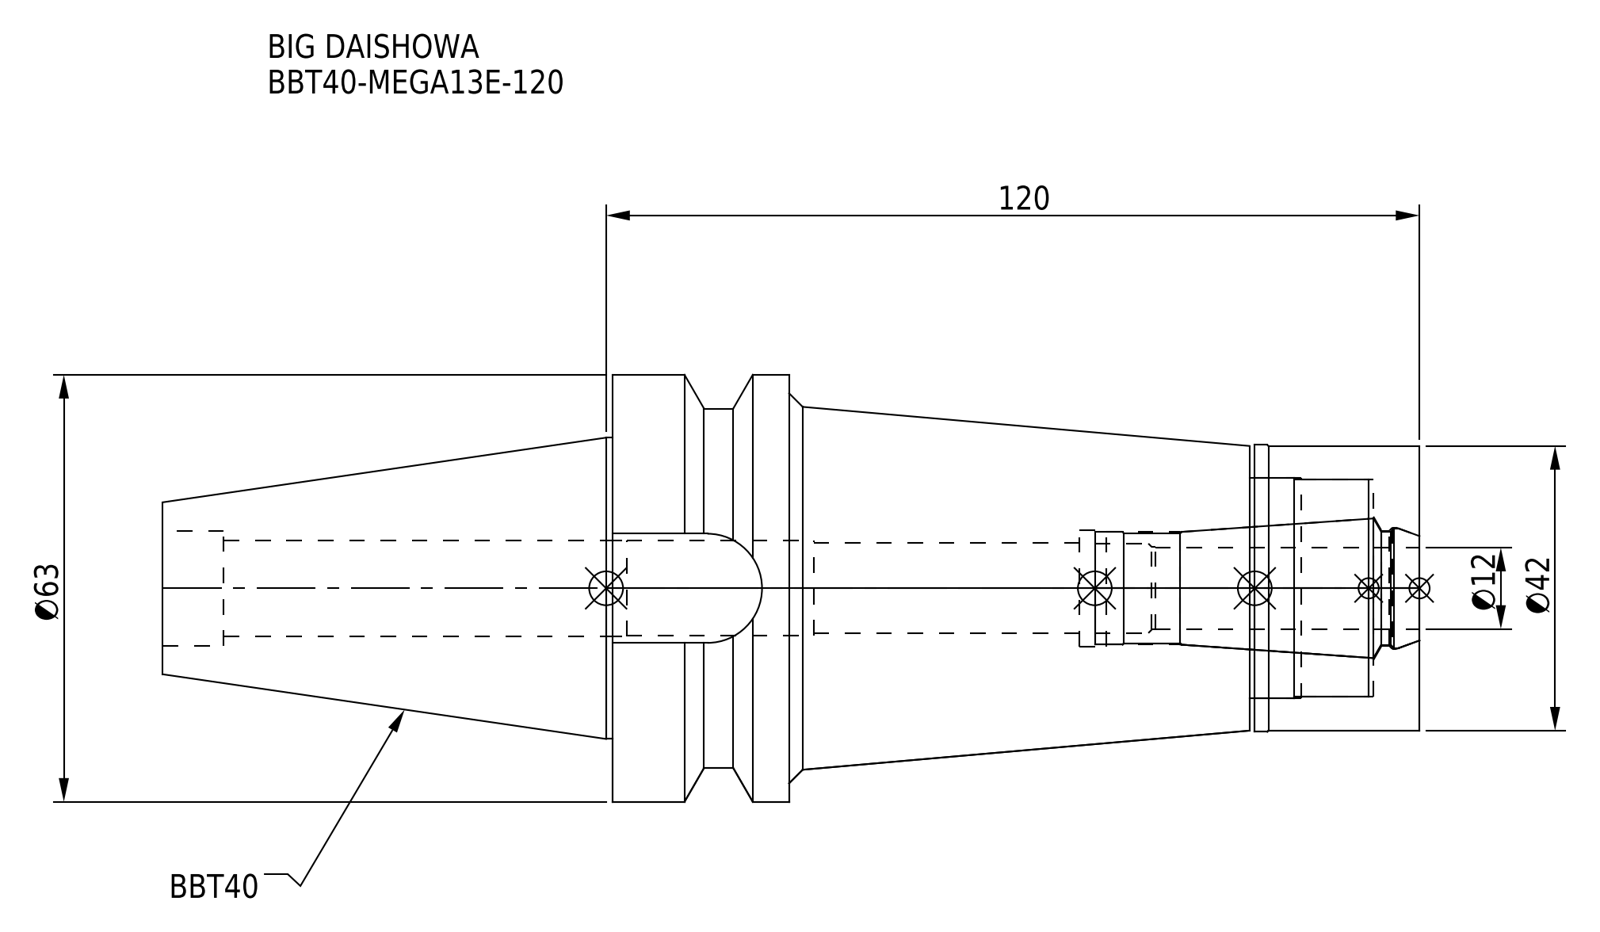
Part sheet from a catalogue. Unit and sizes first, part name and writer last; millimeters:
Units: millimetres
Overall size (bounding box): 185.4 × 63 × 63
Round holes (diameter × count): ⌀13.3 ×1, ⌀14 ×1, ⌀14.2 ×1, ⌀16.6 ×1, ⌀17 ×1, ⌀17.2 ×1, ⌀17.9 ×1, ⌀32 ×1, ⌀32.5 ×1
Round bosses / shafts (diameter × count): ⌀63 ×1, ⌀53 ×1, ⌀44.45 ×1, ⌀42.3 ×1, ⌀42 ×1
Partial cylindrical surfaces — rounded edges, fillets, slot ends (radius × count): R8.05 ×1
Main face-to-face distances: 119, 25.1, 24.3, 94.7, 0.8, 93.9, 93, 68.7, 67.9, 26
Volume: 259 283 mm³ · Surface area: 45 532 mm²
Bodies: 2 solids, 81 faces (21 planar, 40 cylindrical, 20 other)
Part name (STEP PRODUCT): BBT40-MEGA13E-120-120.stp; DXF_TEMP_ASSY_ASM_4_ASM.stp; BBT40-MEGA13E-120; BBT40-MEGA13E-120_1.stp (+3 more)
STEP written by: SolidWorks 2019 (CONFIG_CONTROL_DESIGN)
